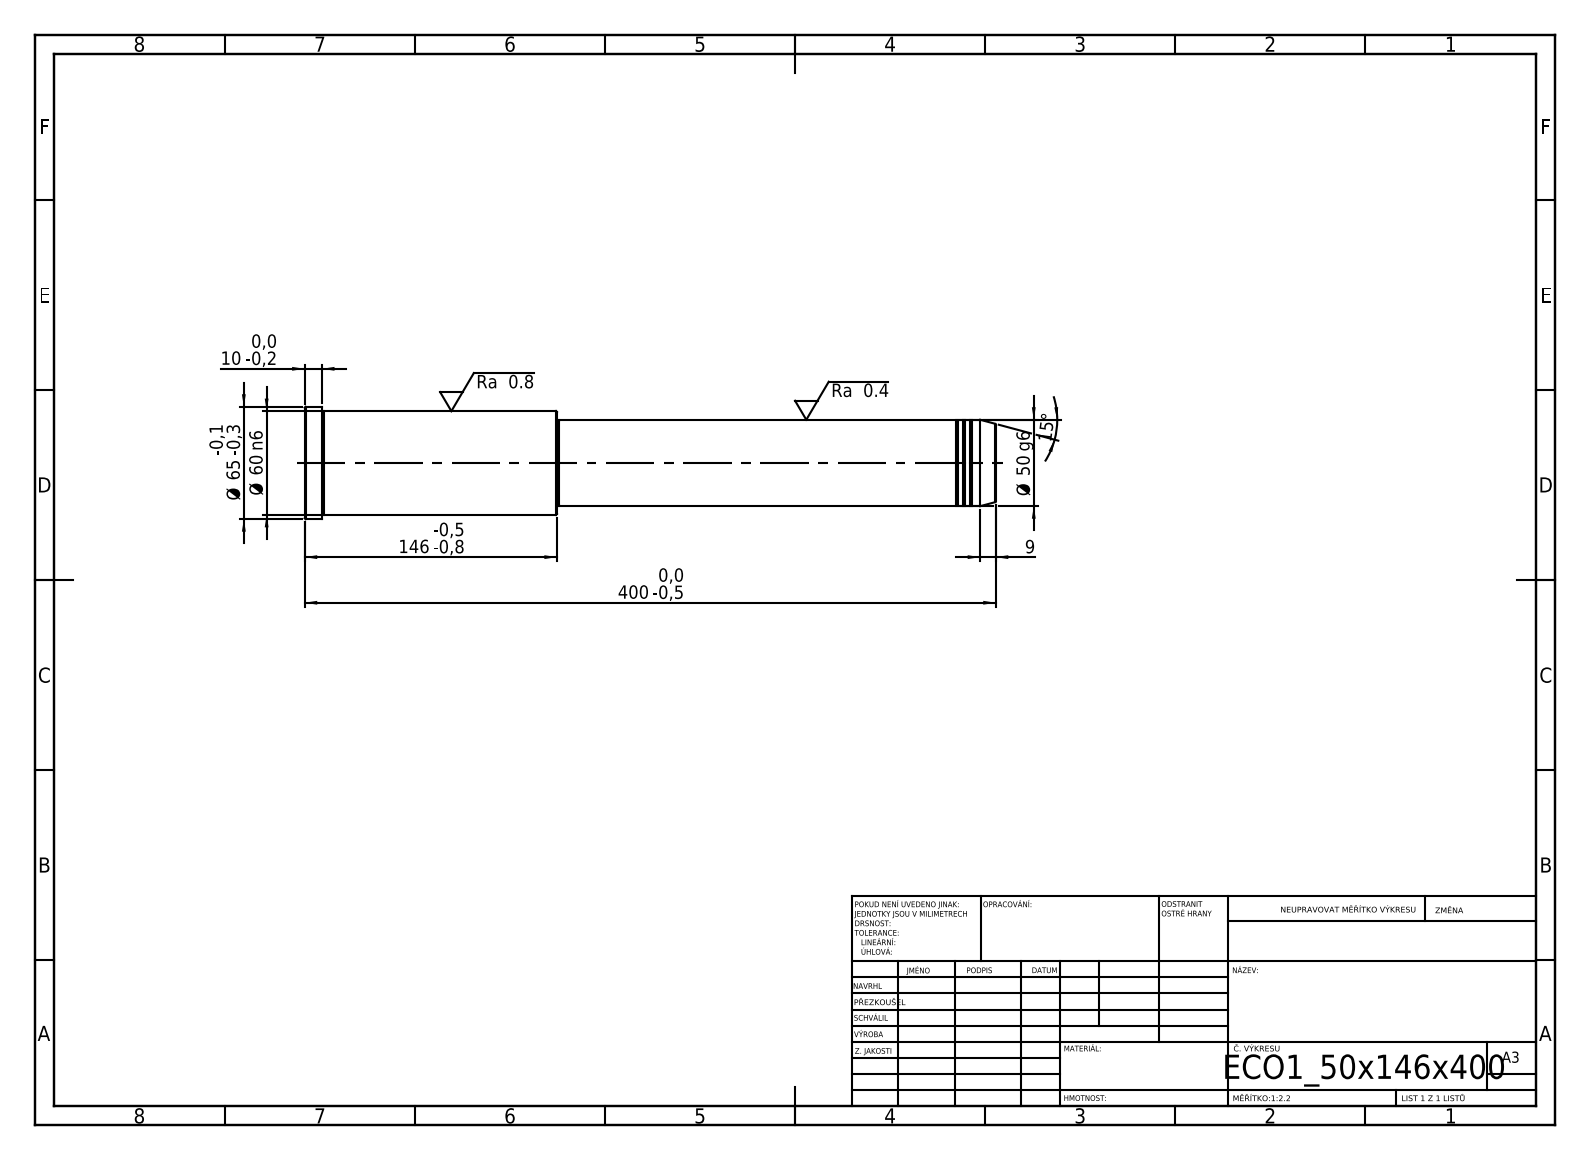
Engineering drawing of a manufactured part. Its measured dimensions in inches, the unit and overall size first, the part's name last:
Units: inches
Overall size (bounding box): 15.748 × 2.559 × 2.559
Round bosses / shafts (diameter × count): ⌀2.559 ×1, ⌀2.362 ×1, ⌀1.969 ×1, ⌀1.929 ×1
Main face-to-face distances: 15.748, 10, 5.748, 15.354, 5.354, 0.394, 9.961, 0.039, 5.394, 5.787
Volume: 55.8 in³ · Surface area: 115 in²
Bodies: 1 solid, 43 faces (5 planar, 14 cylindrical, 24 other)
STEP written by: SolidWorks 2019 (CONFIG_CONTROL_DESIGN)
